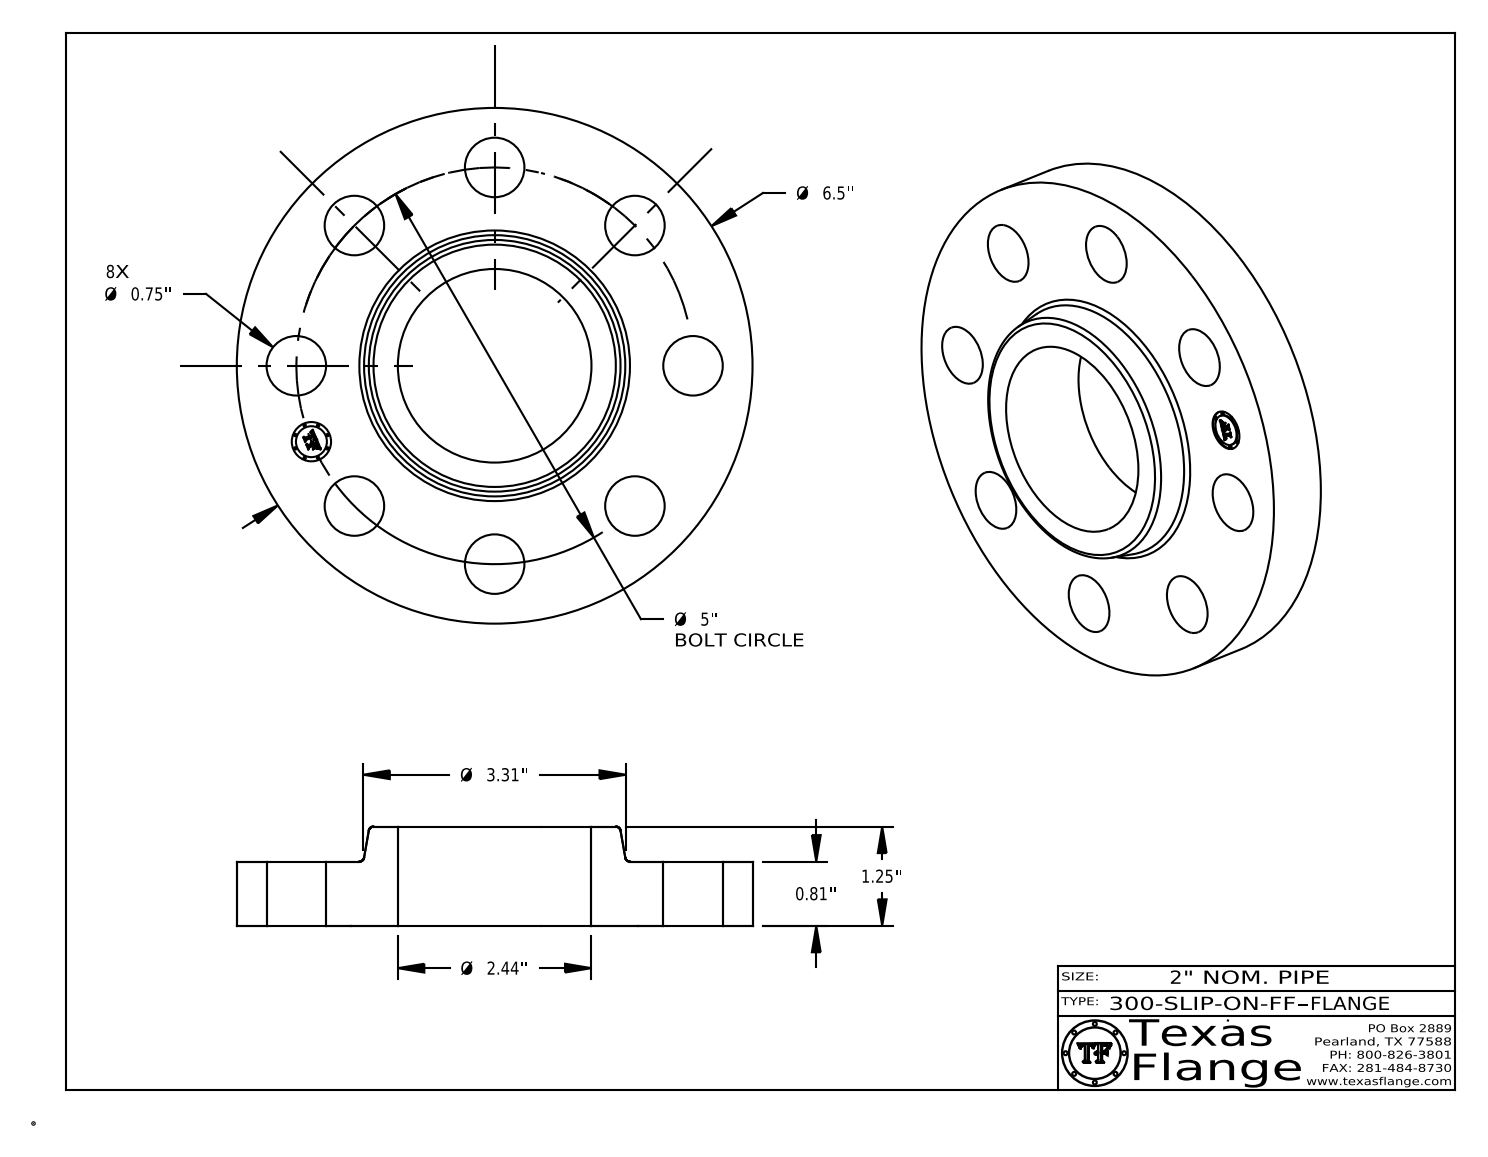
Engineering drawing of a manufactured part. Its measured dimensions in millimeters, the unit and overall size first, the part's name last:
Units: millimetres
Overall size (bounding box): 165.1 × 165.1 × 31.8
Round holes (diameter × count): ⌀19.1 ×8, ⌀12.6 ×1, ⌀62 ×1
Round bosses / shafts (diameter × count): ⌀0.8 ×8, ⌀165.1 ×1, ⌀9.9 ×1
Main face-to-face distances: 20.6, 31.8, 11.2, 20.2, 0.4, 11.6, 3.8, 3.7, 0.7, 2.4
Hole centre spacings: 63.5, 48.6, 89.8, 117.3, 127, 24.8, 70.6, 105.6
Volume: 356 900 mm³ · Surface area: 61 190 mm²
Bodies: 1 solid, 415 faces (369 planar, 40 cylindrical, 6 other)
Part name (STEP PRODUCT): 300-SLIP-ON-FF
STEP written by: CATIA V5 STEP AP214 (AUTOMOTIVE_DESIGN)
